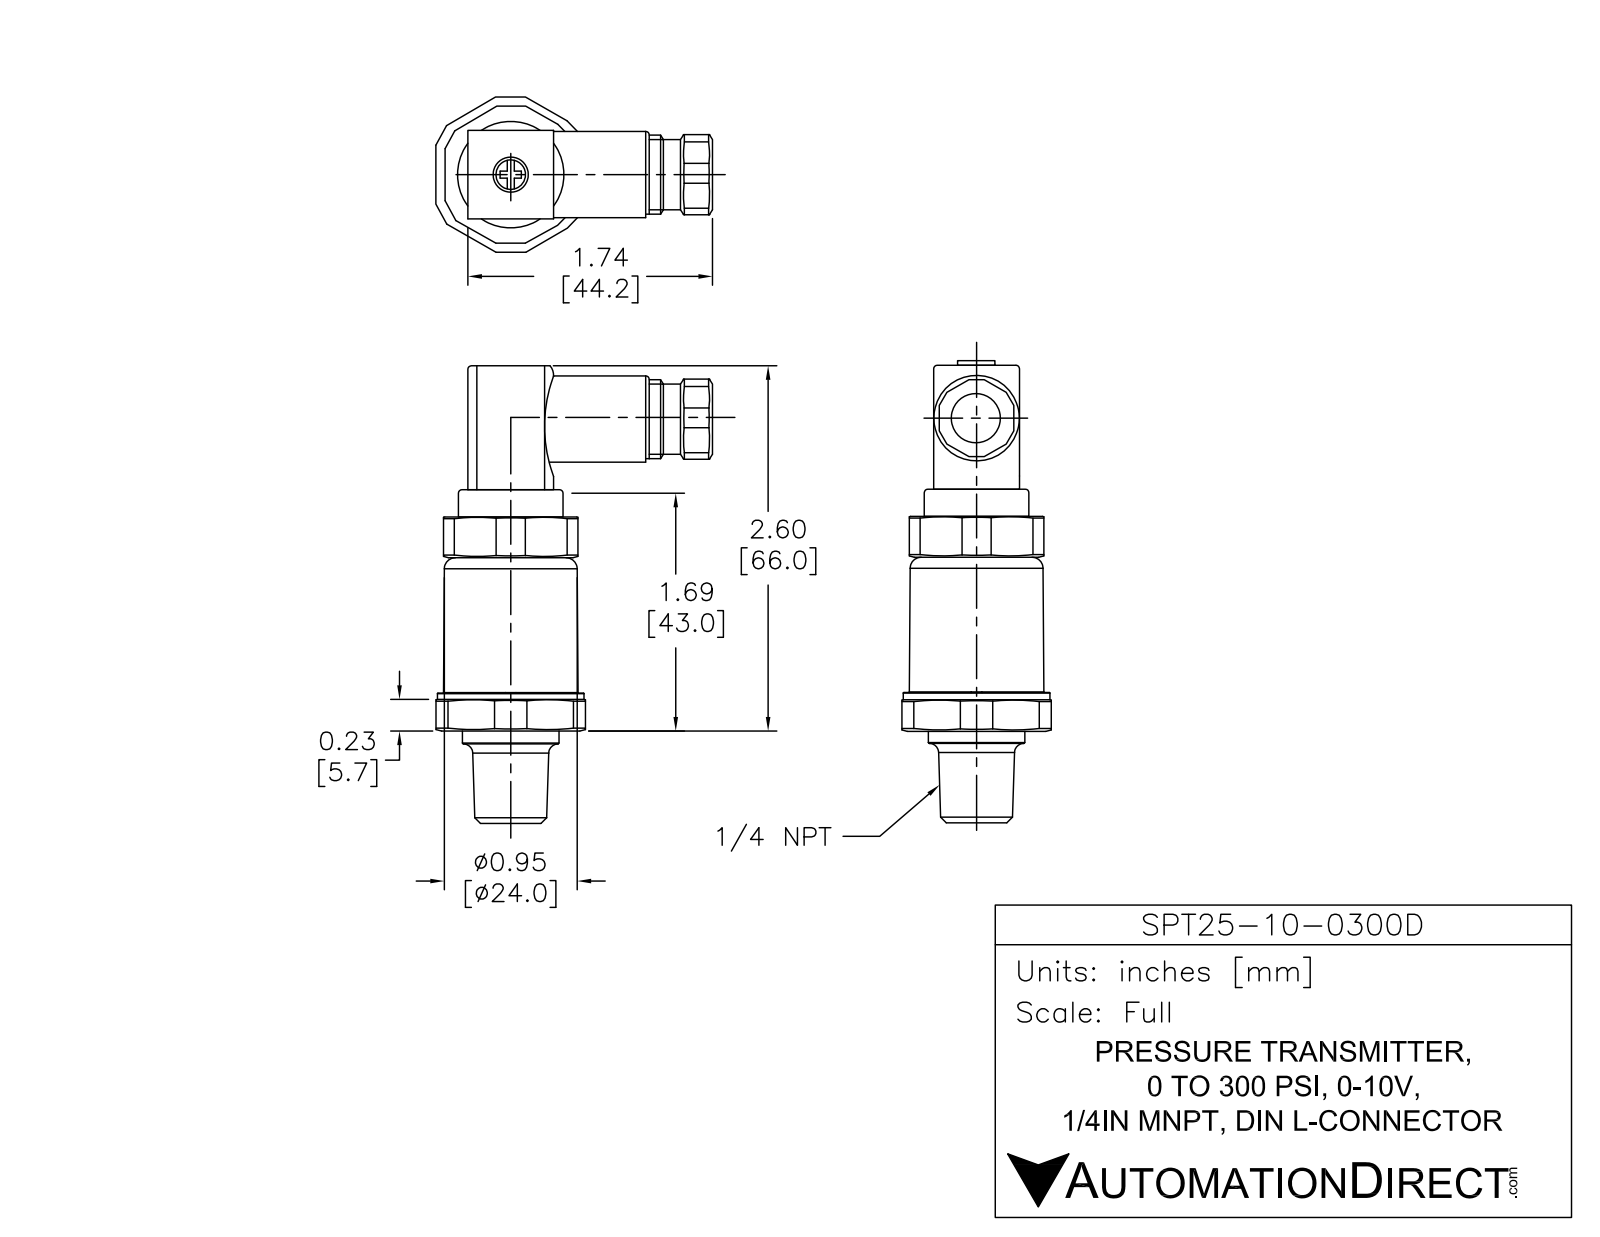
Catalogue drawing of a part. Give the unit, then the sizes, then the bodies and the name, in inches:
Units: inches
Overall size (bounding box): 3.199 × 1.496 × 1.406
Round holes (diameter × count): ⌀0.039 ×1, ⌀0.13 ×1, ⌀0.276 ×1, ⌀0.315 ×1
Round bosses / shafts (diameter × count): ⌀1.053 ×1, ⌀0.945 ×1, ⌀0.689 ×1, ⌀0.591 ×1, ⌀0.551 ×1, ⌀0.433 ×1
Partial cylindrical surfaces — rounded edges, fillets, slot ends (radius × count): R0.059 ×8, R0.045 ×4, R0.089 ×4, R0.079 ×3, R0.045 ×1, R0.046 ×1, R0.571 ×1
Main face-to-face distances: 0.059, 1.161, 1.22, 0.62, 0.014, 0.606, 0.266, 1.486, 1.427, 0.197
Hole centre spacings: 0.052
Volume: 1.702 in³ · Surface area: 15.71 in²
Bodies: 5 solids, 200 faces (96 planar, 87 cylindrical, 17 other)
Part name (STEP PRODUCT): SPT25-10-0300D
STEP written by: SolidWorks 2013 (AUTOMOTIVE_DESIGN)
